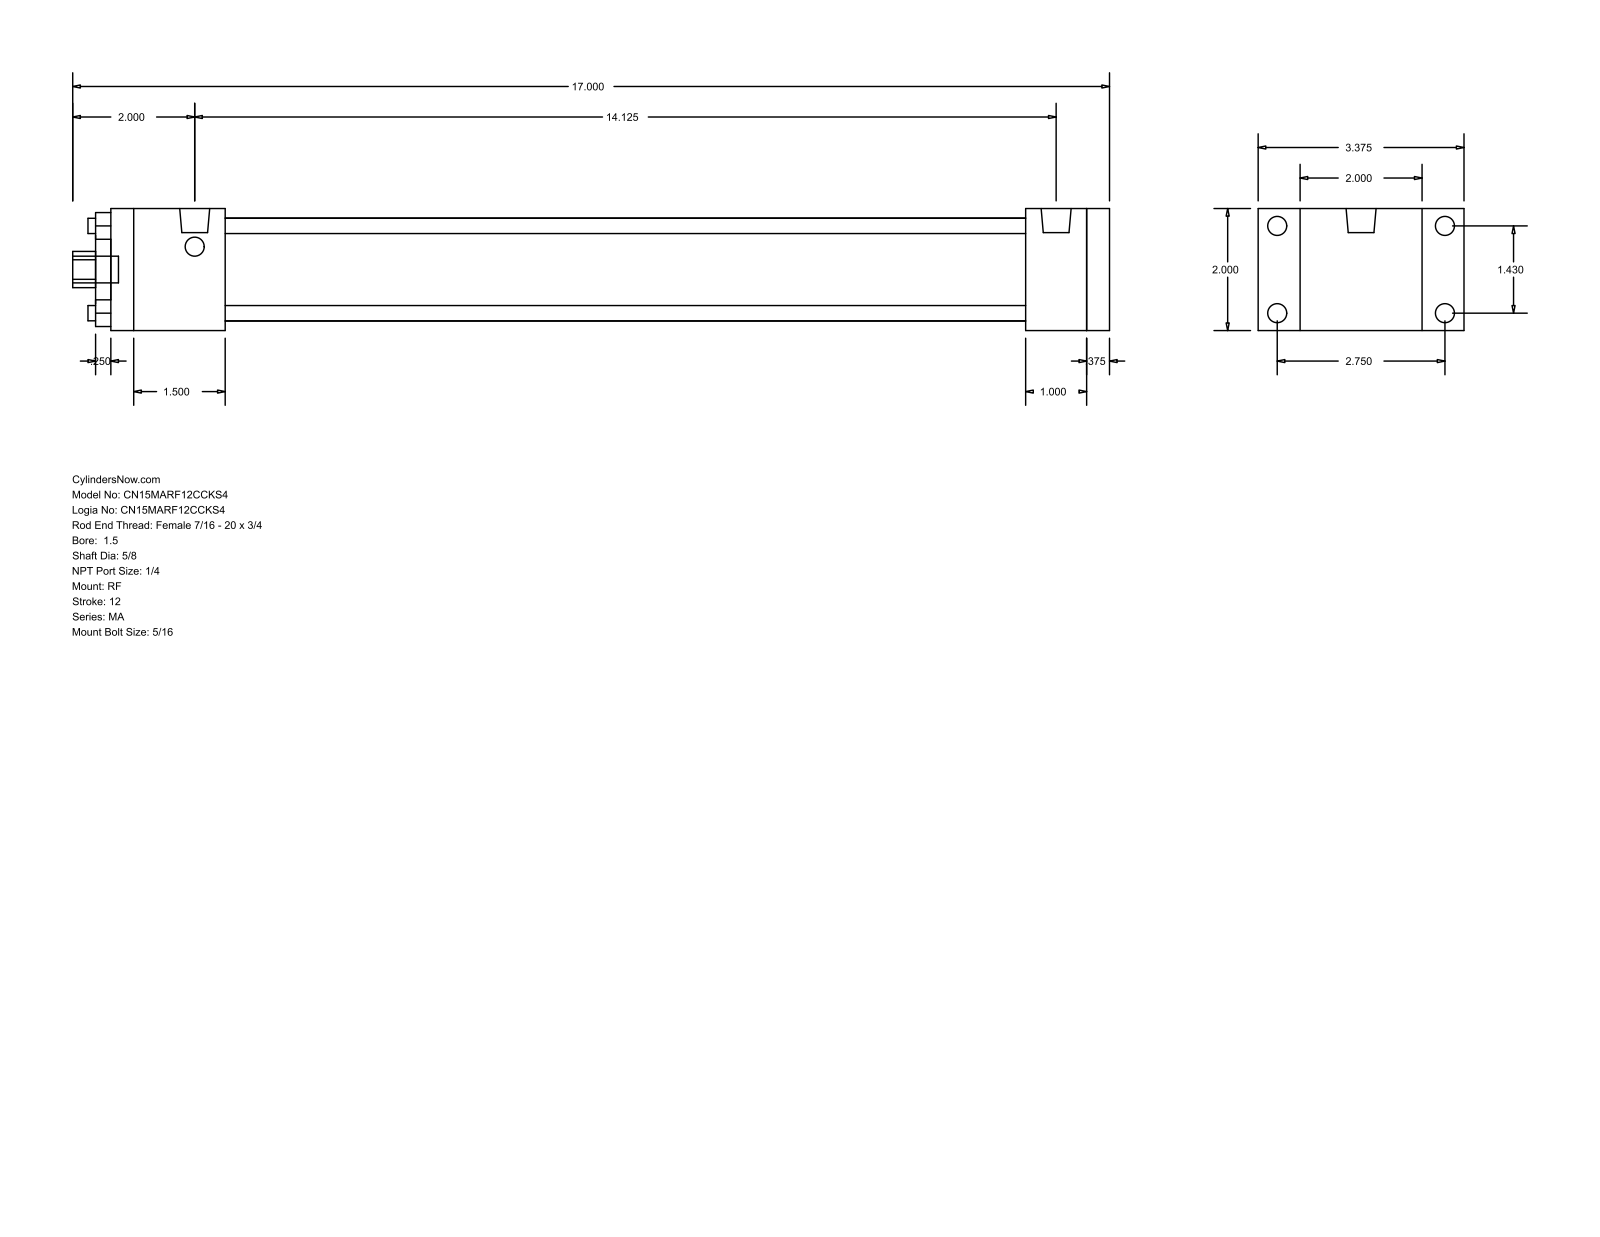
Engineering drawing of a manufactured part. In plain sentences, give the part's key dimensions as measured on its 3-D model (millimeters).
The part is named "MA_RF__0150_0.625". Its 3-D file was written by "GSSL Pune (CONFIG_CONTROL_DESIGN)". It is 0 solids with 92 faces: 64 planar, 28 cylindrical and 0 other. Overall it measures 431.8 by 85.72 by 50.8 millimeters. Round holes: 4 of diameter 6.35, 1 of diameter 15.88, 1 of diameter 28.57, 1 of diameter 42.93. Round bosses or shafts: 8 of diameter 7.94, 2 of diameter 12.49, 1 of diameter 11.11. Partial cylindrical surfaces (rounded edges, fillets, slot ends): 1 of radius 7.54. The main face-to-face distances are 50.8, 9.53, 415.92, 406.39, 381, 25.39, 34.92, 47.62, 333.38, 358.77. The hole center spacings are 25.68, 36.32, 51.36.
